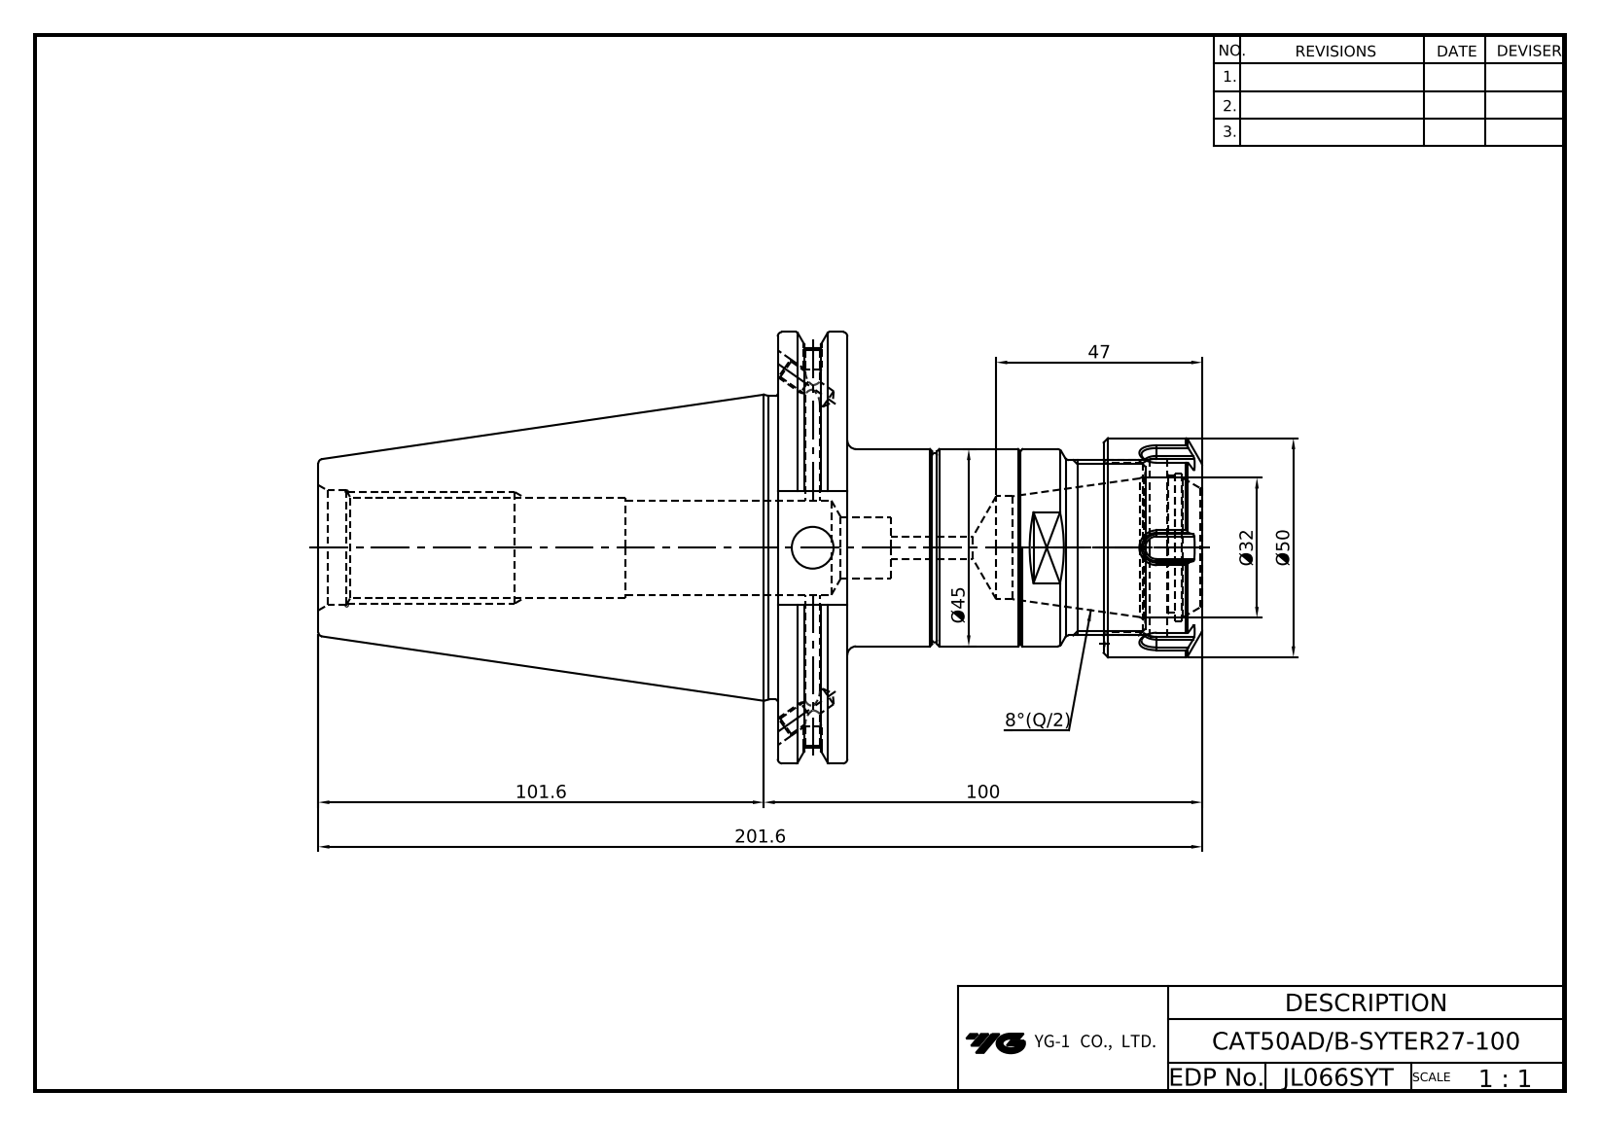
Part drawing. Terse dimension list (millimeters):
name: LO-CAT50ADB-SYTER27-100; SYNCHRO-ER32-42; SYTER27-COVER(BLUE); ER32NUT
written by: Autodesk Inventor 2022 (AUTOMOTIVE_DESIGN)
unit: mm
bodies: 4 solids, 256 faces (98 planar, 74 cylindrical, 84 other)
size: 201.6 × 98.42 × 94.69
volume: 412 134 mm³; area: 78 766 mm²
holes: 6× ⌀5, 4× ⌀5.1, 2× ⌀3.24, 2× ⌀4.13, 2× ⌀4.2, 1× ⌀1, 1× ⌀4.92, 1× ⌀6.2, 1× ⌀6.5, 1× ⌀9.53, 1× ⌀14, 1× ⌀15
bosses: 2× ⌀45, 1× ⌀98.42, 1× ⌀91.29, 1× ⌀69.25, 1× ⌀50, 1× ⌀41, 1× ⌀40, 1× ⌀38.4
rounds: 12× R0.5
face distances: 15.88, 22.5, 26, 13.1, 40.13, 24.25, 40.33, 24.45, 96.83, 80.95
hole spacings: 12.5, 17.68, 12.53, 25, 25.3, 0.64, 0.8, 1.18
